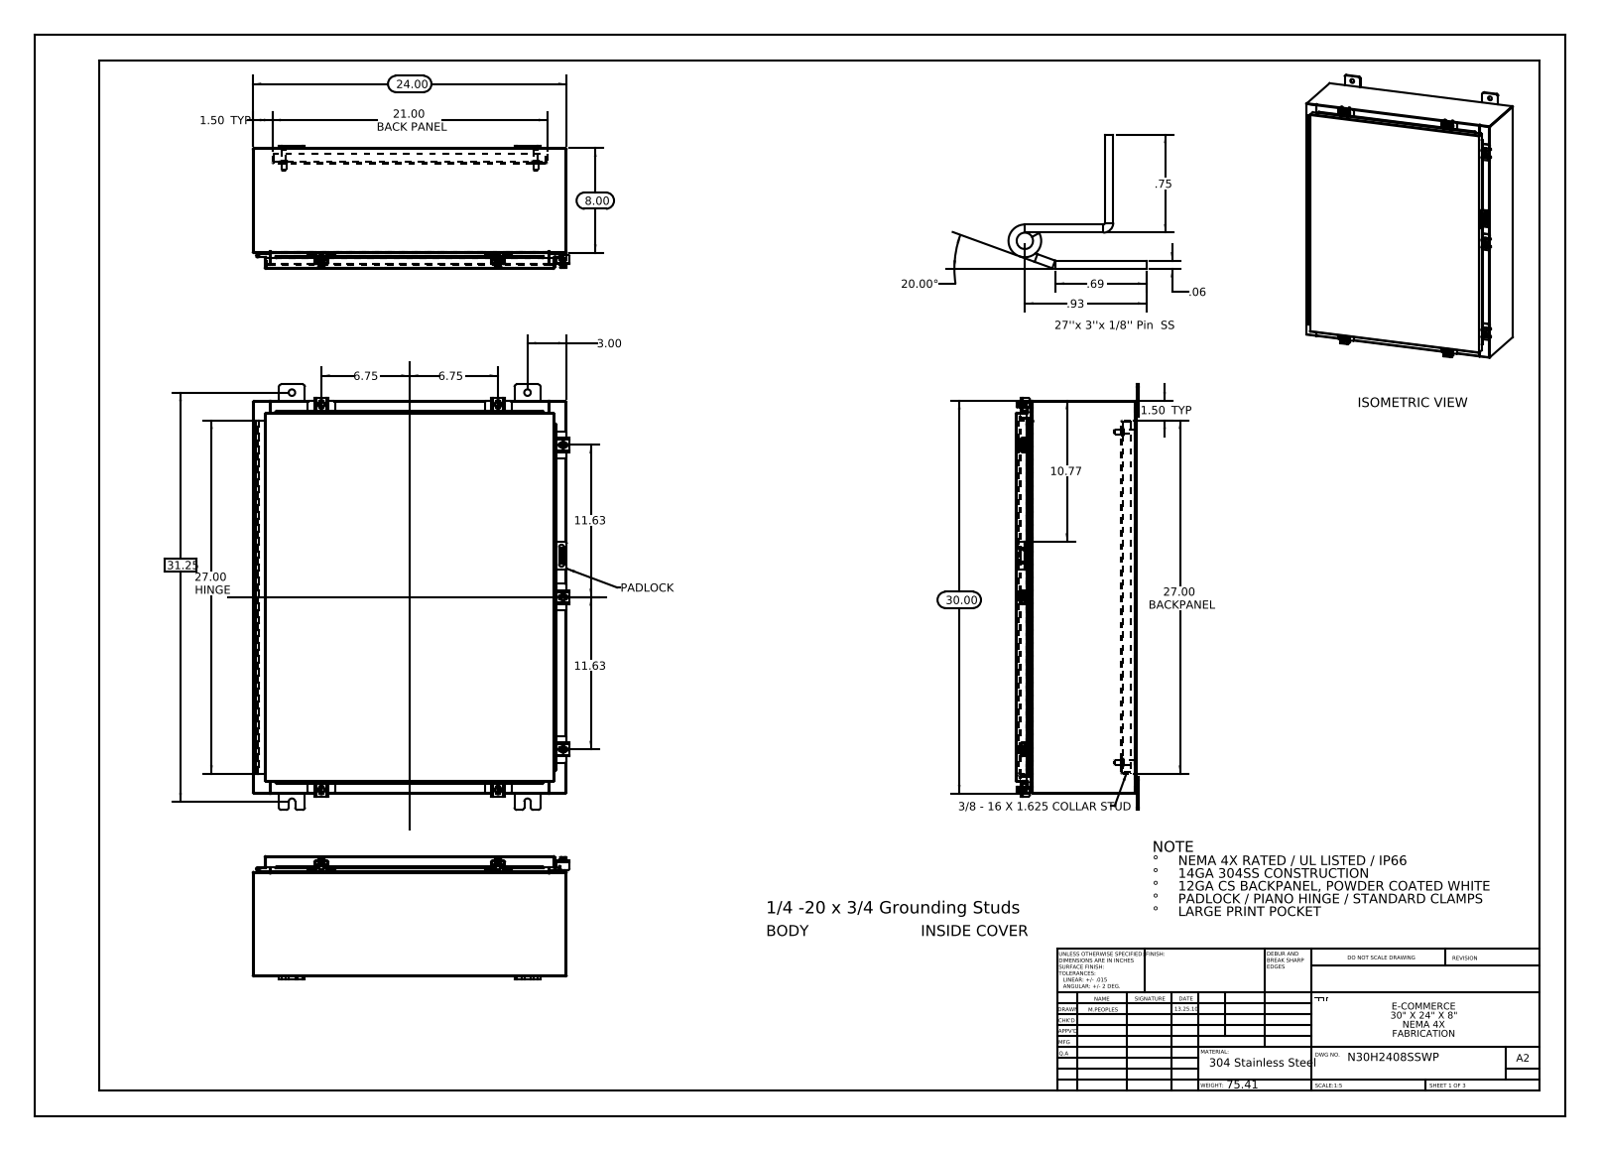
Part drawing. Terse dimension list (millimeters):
name: N30H2408SSWP Standard Clamps; N30H2408SSWP Backpanel; N30H2408SSWP Body; N30H2408SSWP Clamp Bracket (+8 more)
written by: SolidWorks 2013 (CONFIG_CONTROL_DESIGN)
unit: mm
bodies: 52 solids, 1990 faces (1056 planar, 830 cylindrical, 104 other)
size: 825.5 × 615 × 238.5
volume: 4 339 000 mm³; area: 4 270 000 mm²
holes: 8× ⌀12.7, 7× ⌀5.4, 7× ⌀6.6, 2× ⌀3.2, 1× ⌀3.2
bosses: 8× ⌀6.4, 7× ⌀12.7, 7× ⌀10.1, 4× ⌀15.9, 4× ⌀9.5, 4× ⌀8.4
rounds: 34× R1.5, 27× R0.3, 24× R4.8, 21× R2.2, 14× R3, 14× R3.6, 11× R1.3, 10× R2
face distances: 1.9, 231.8, 233.7, 229.9, 2.6, 25.4, 27.3, 204.5, 206.4, 29.9
hole spacings: 698.5, 809.7, 47.2, 57.8, 59.1, 61.5, 90.4, 90.4
